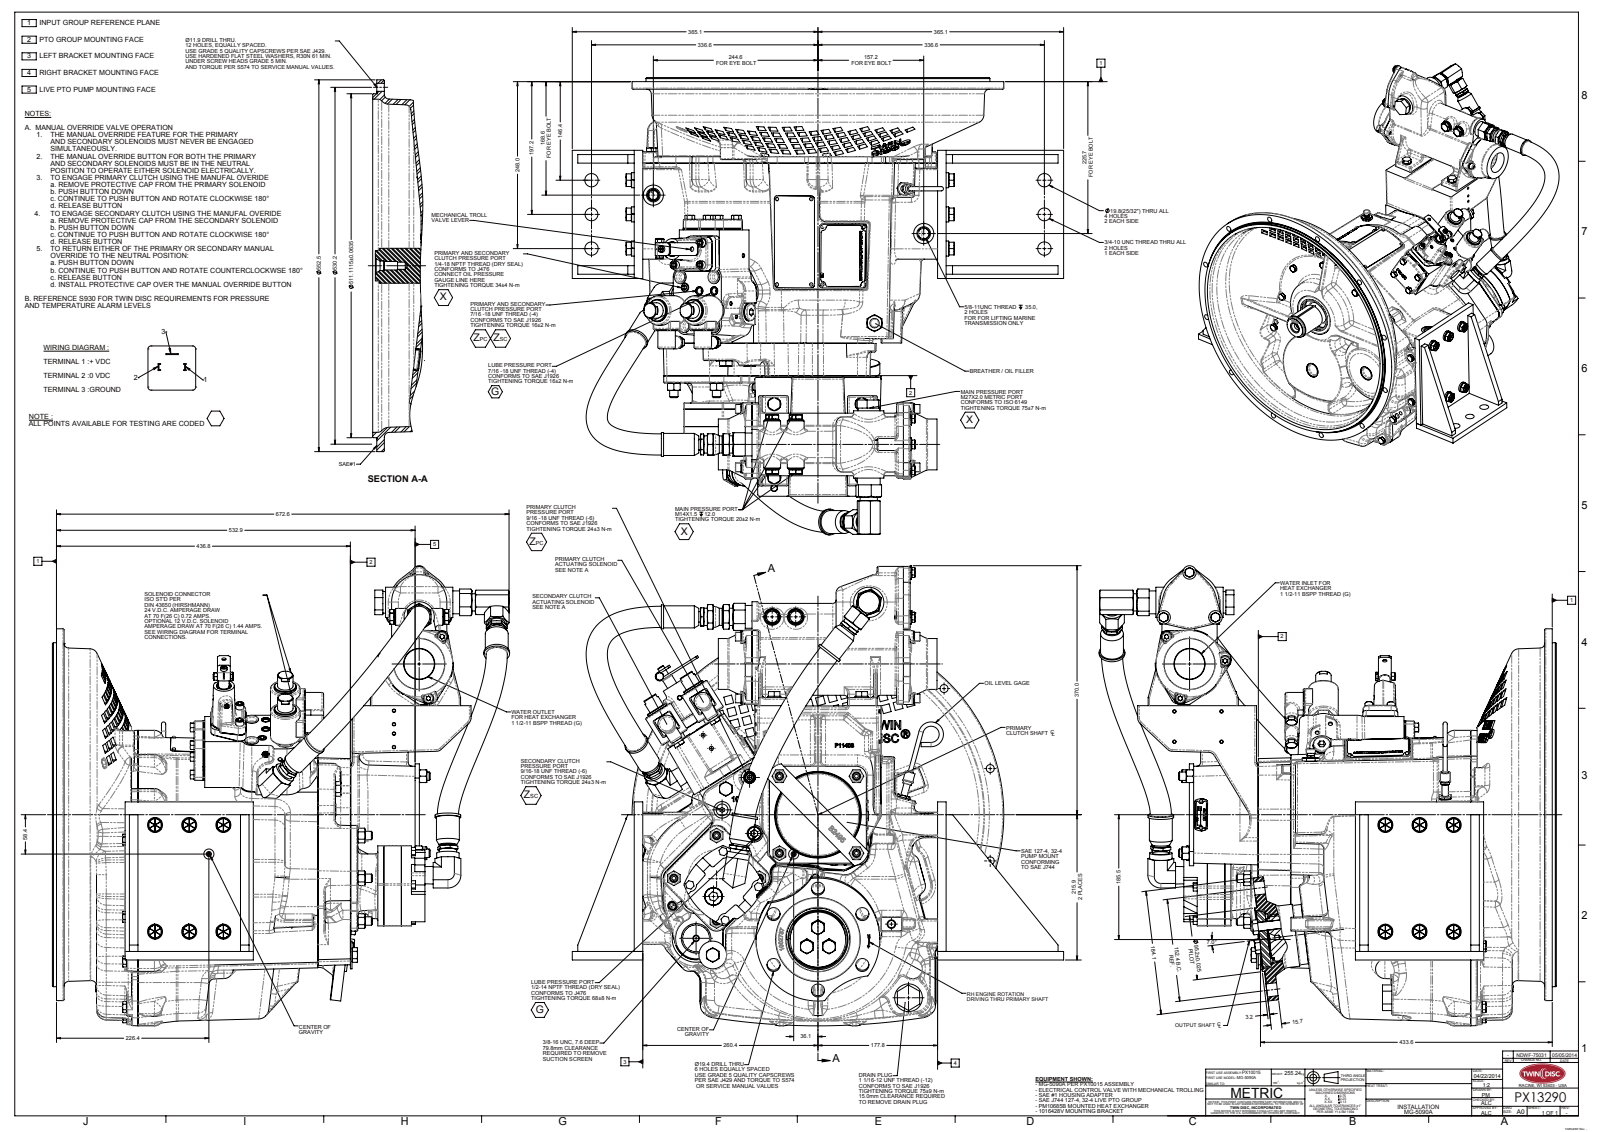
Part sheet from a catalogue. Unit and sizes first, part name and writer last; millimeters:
Units: millimetres
Overall size (bounding box): 730.25 × 683.69 × 679.47
Round holes (diameter × count): ⌀11.91 ×12, ⌀5 ×8, ⌀19.45 ×6, ⌀19.84 ×4, ⌀6.2 ×3, ⌀7.94 ×3, ⌀6.8 ×2, ⌀10 ×2, ⌀11.13 ×2, ⌀16.67 ×2, ⌀19.05 ×2, ⌀24.61 ×2
Round bosses / shafts (diameter × count): ⌀12.54 ×8, ⌀22.33 ×6, ⌀13 ×6, ⌀18.87 ×5, ⌀14.14 ×5, ⌀19.85 ×4, ⌀19 ×4, ⌀25 ×3
Partial cylindrical surfaces — rounded edges, fillets, slot ends (radius × count): R2.5 ×63, R2 ×49, R2.03 ×43, R8.13 ×38, R3.05 ×35, R5 ×32, R1.52 ×27, R12.7 ×27
Main face-to-face distances: 12.7, 0.78, 48.54, 450.85, 165.1, 47.76, 438.15, 267.33, 268.11, 315.87
Hole centre spacings: 76.2, 459.18, 137.23, 265.1, 265.11, 374.92, 512.14, 131.98
Bodies: 0 solids, 5012 faces (1683 planar, 1146 cylindrical, 2183 other)
Part name (STEP PRODUCT): PX13290
STEP written by: SolidWorks 2010 (AUTOMOTIVE_DESIGN)
